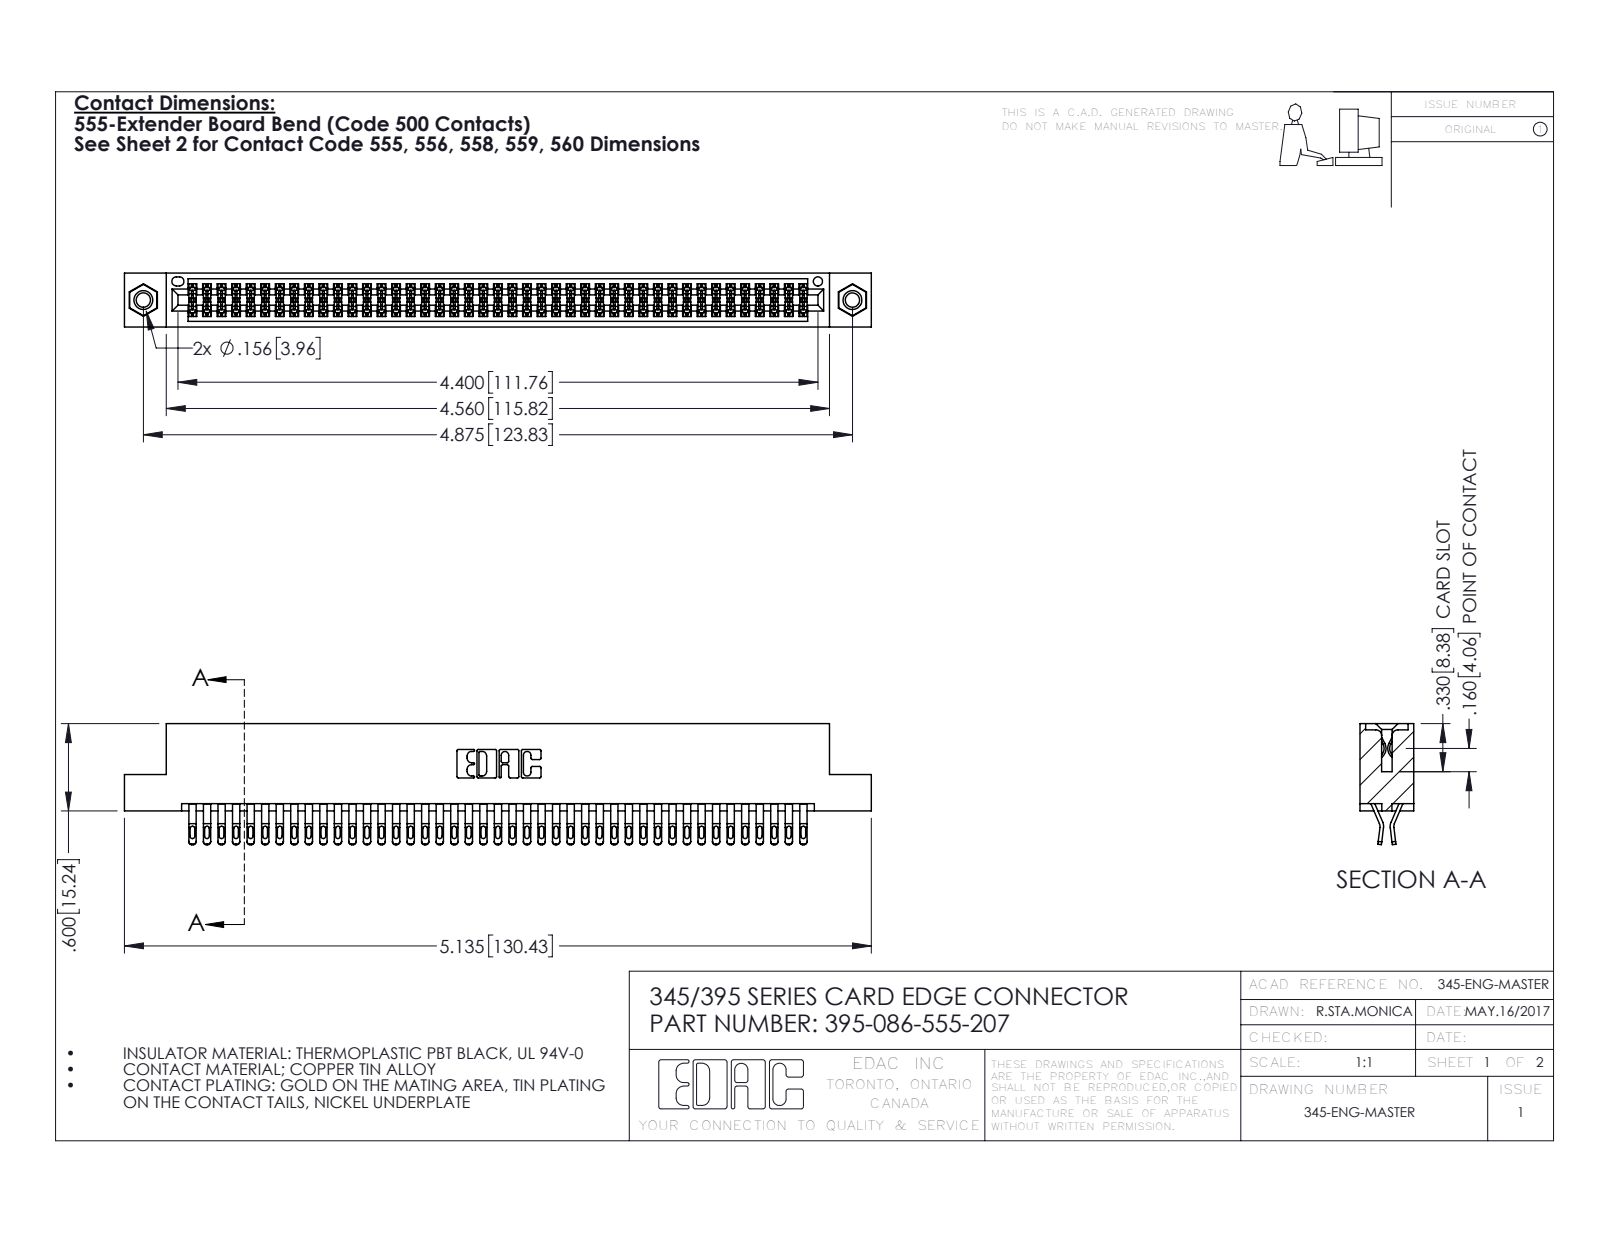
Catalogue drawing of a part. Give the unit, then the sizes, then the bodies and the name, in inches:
Units: inches
Overall size (bounding box): 5.135 × 0.832 × 0.37
Round holes (diameter × count): ⌀0.098 ×2, ⌀0.125 ×2, ⌀0.156 ×2, ⌀0.064 ×1
Round bosses / shafts (diameter × count): ⌀0.155 ×2
Partial cylindrical surfaces — rounded edges, fillets, slot ends (radius × count): R0.016 ×215, R0.02 ×172, R0.006 ×129, R0.01 ×22, R0.007 ×6, R0.031 ×6, R0.026 ×3, R0.01 ×2
Main face-to-face distances: 0.072, 0.298, 0.025, 0.37, 0.2, 0.098, 0.272, 0.225, 0.175, 0.149
Hole centre spacings: 0.27, 4.639, 4.875
Volume: 0.788 in³ · Surface area: 31.01 in²
Bodies: 89 solids, 5002 faces (2778 planar, 2208 cylindrical, 16 other)
Part name (STEP PRODUCT): 345 Part_Flush Mounting Lugs - 0.156 Dia-TI; 345-292-001_555 Tail; 395-086-555-207; 345-250-001_345-250-005-103
STEP written by: SolidWorks 2016 (CONFIG_CONTROL_DESIGN)
